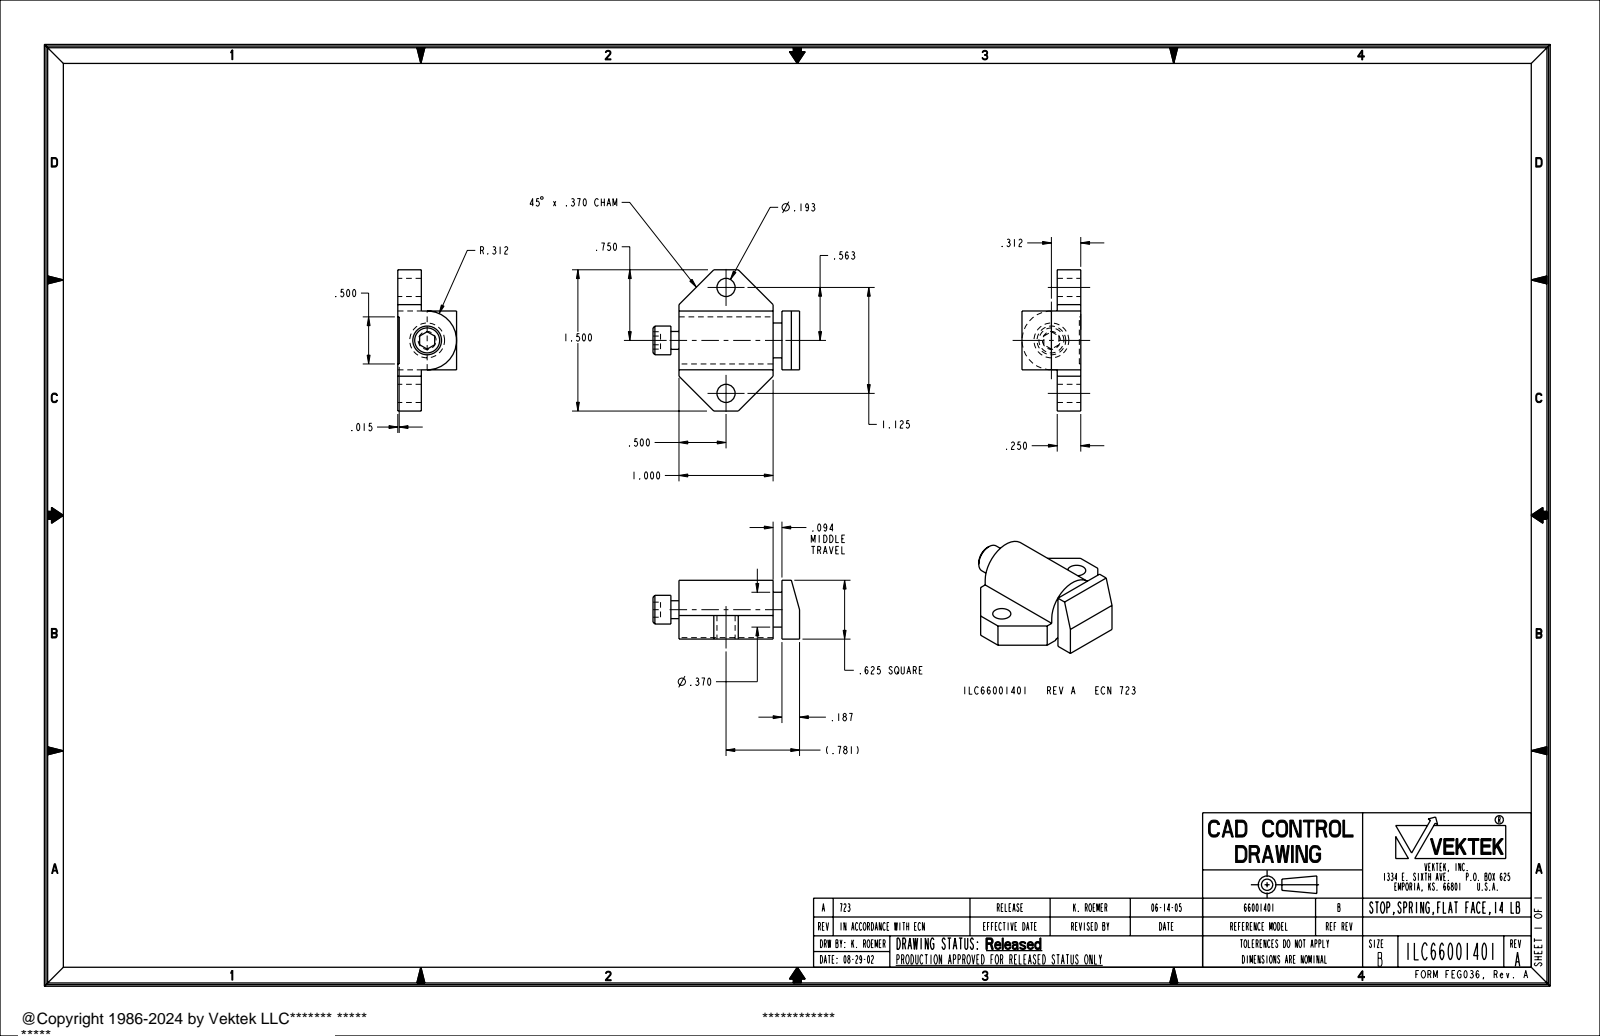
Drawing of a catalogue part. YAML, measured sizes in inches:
part_name: "ILC66001401"
step_written_by: "PRO/ENGINEER BY PARAMETRIC TECHNOLOGY CORPORATION, 2004290 (AUTOMOTIVE_DESIGN_CC2)"
units: inches
bodies: {solids: 1, faces: 46, planar: 33, cylindrical: 11, other: 2}
overall_size: [1.557, 1.5, 0.625]
volume: 0.565
surface_area: 5.974
round_holes:
  - {diameter: 0.193, count: 2}
round_bosses_or_shafts:
  - {diameter: 0.37, count: 1}
  - {diameter: 0.305, count: 1}
  - {diameter: 0.19, count: 1}
partial_cylinders:
  - {radius: 0.312, count: 1}
face_to_face_distances: [0.25, 0.015, 0.235, 1, 1.094, 0.094, 1.244, 0.187, 0.281, 1.281]
hole_center_spacings: [1.125]
